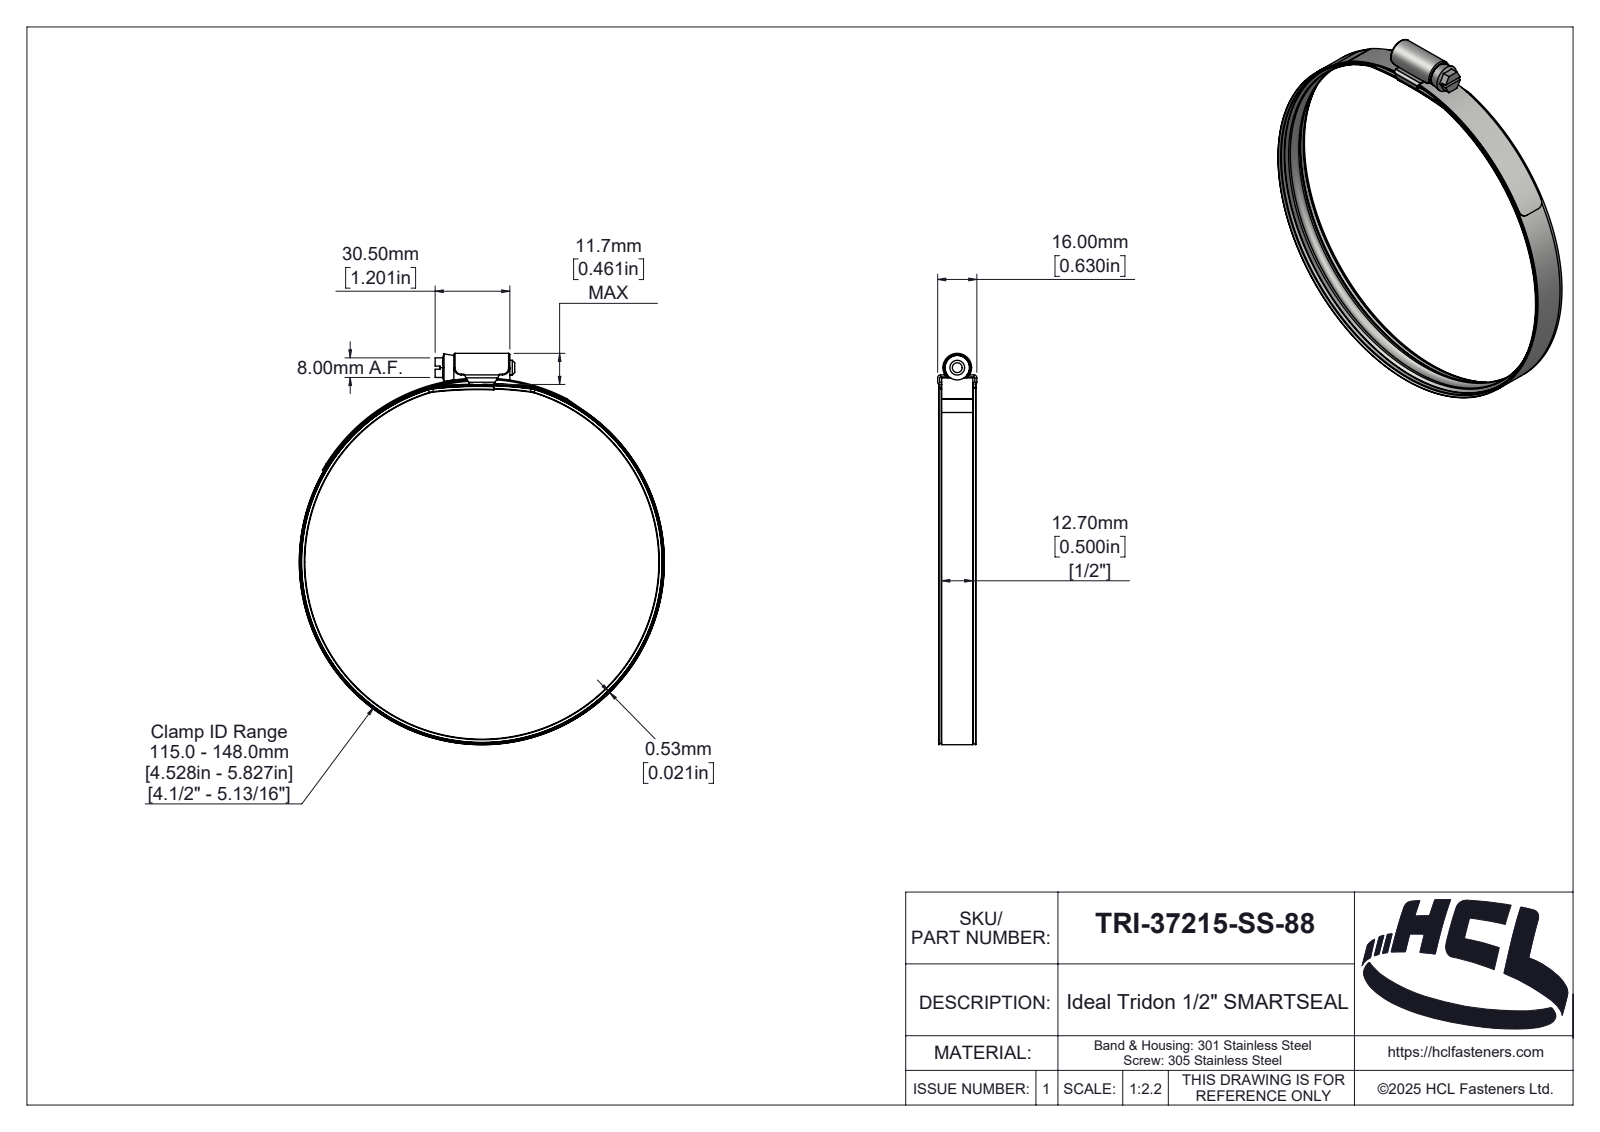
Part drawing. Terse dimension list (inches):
name: TRI-37215-SS-88
written by: SolidWorks 2025 (AUTOMOTIVE_DESIGN)
unit: in
bodies: 4 solids, 418 faces (42 planar, 119 cylindrical, 257 other)
size: 6.289 × 5.869 × 0.63
volume: 0.508 in³; area: 51.98 in²
holes: 1× ⌀5.803, 1× ⌀5.827
bosses: 1× ⌀5.869, 1× ⌀5.819, 1× ⌀0.394, 1× ⌀0.236
rounds: 6× R0.02, 4× R0.118, 2× R0.004, 2× R0.035, 2× R0.047, 2× R0.39, 2× R0.398, 1× R0.018
face distances: 0.5, 0.031, 0.122, 0.021, 0.091, 1.201, 0.154, 0.065, 0.565, 0.598
